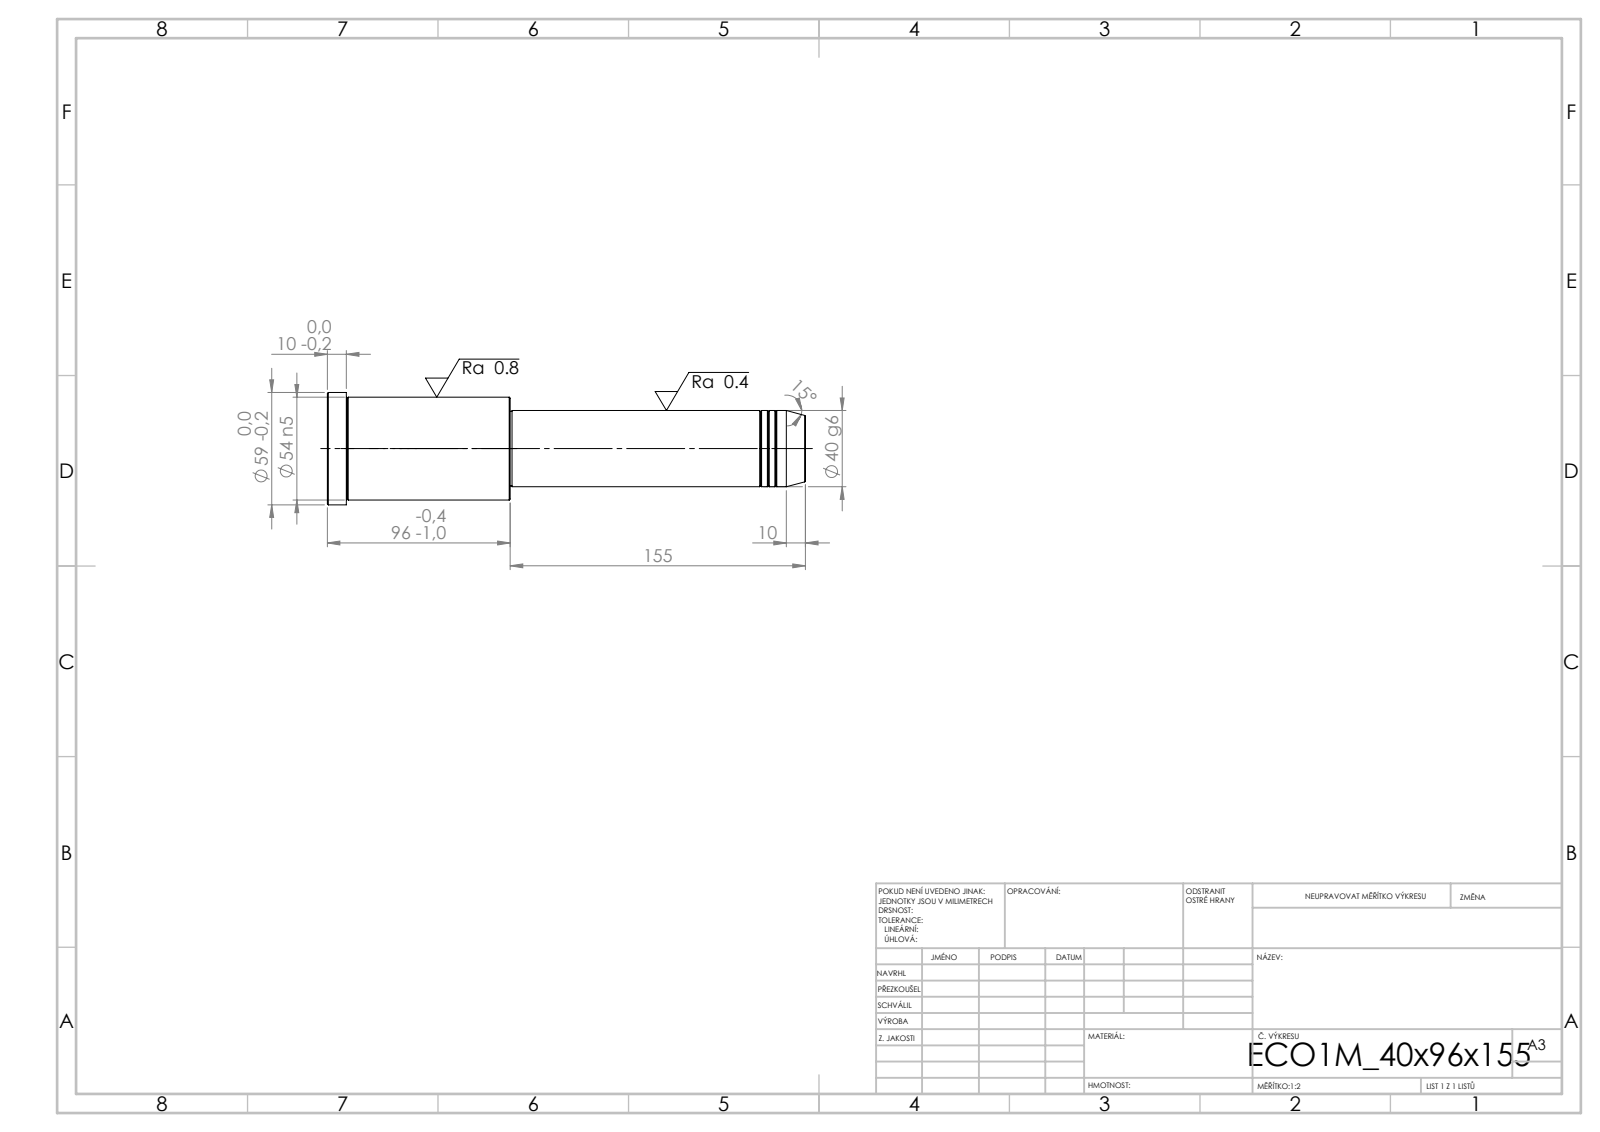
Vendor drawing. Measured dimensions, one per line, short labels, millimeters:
written by: SolidWorks 2019 (CONFIG_CONTROL_DESIGN)
unit: mm
bodies: 1 solid, 43 faces (5 planar, 14 cylindrical, 24 other)
size: 251 × 59 × 59
volume: 417 147 mm³; area: 41 335 mm²
bosses: 1× ⌀59, 1× ⌀54, 1× ⌀40, 1× ⌀39
face distances: 96, 155, 251, 241, 86, 10, 154, 1, 87, 97
